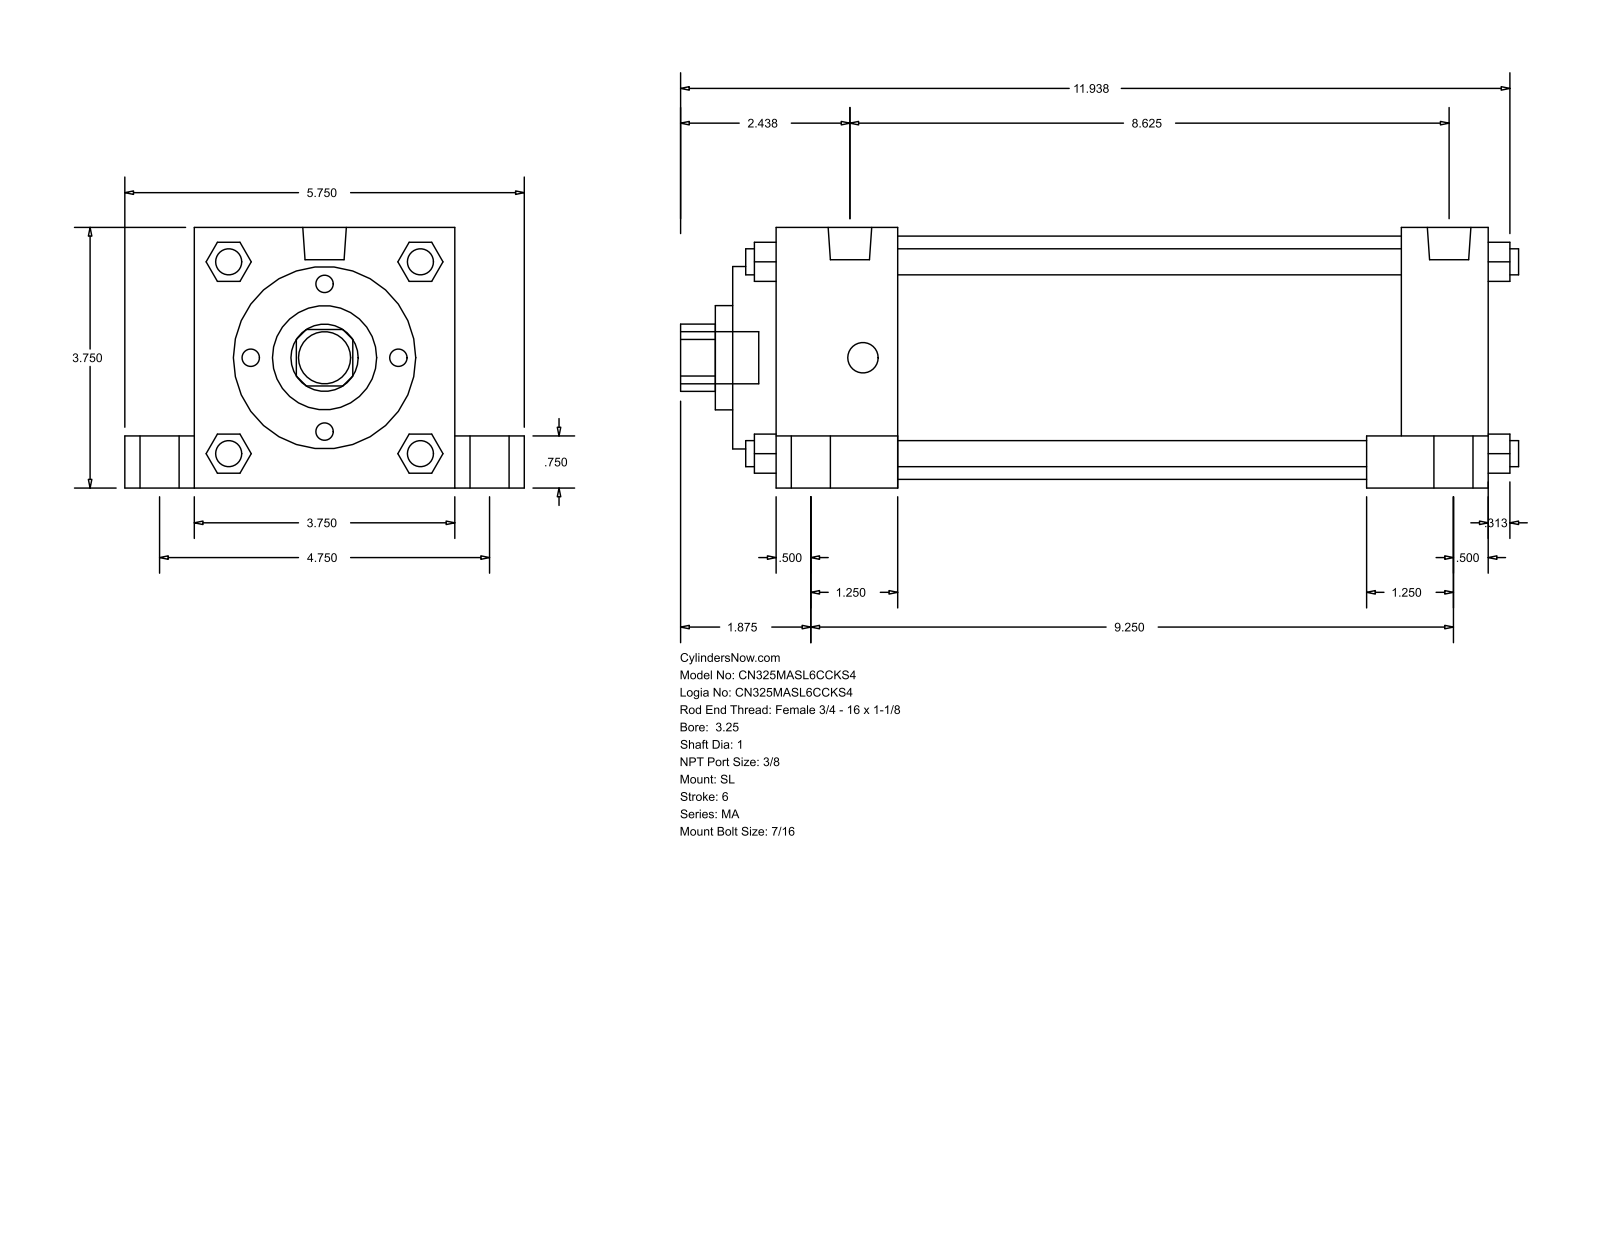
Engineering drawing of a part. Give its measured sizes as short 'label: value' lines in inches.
name: MA_SL__0325_1
written by: GSSL Pune (CONFIG_CONTROL_DESIGN)
unit: in
bodies: 0 solids, 150 faces (113 planar, 37 cylindrical, 0 other)
size: 12.063 × 5.75 × 3.75
holes: 1× ⌀1, 1× ⌀1.5, 1× ⌀2.625, 1× ⌀3.5
bosses: 4× ⌀0.813, 4× ⌀0.563, 4× ⌀0.437, 4× ⌀0.375, 2× ⌀0.627, 1× ⌀0.75
rounds: 1× R0.484
face distances: 3.75, 10.25, 0.625, 1, 4.75, 10.875, 0.75, 9, 1.25, 1.75
